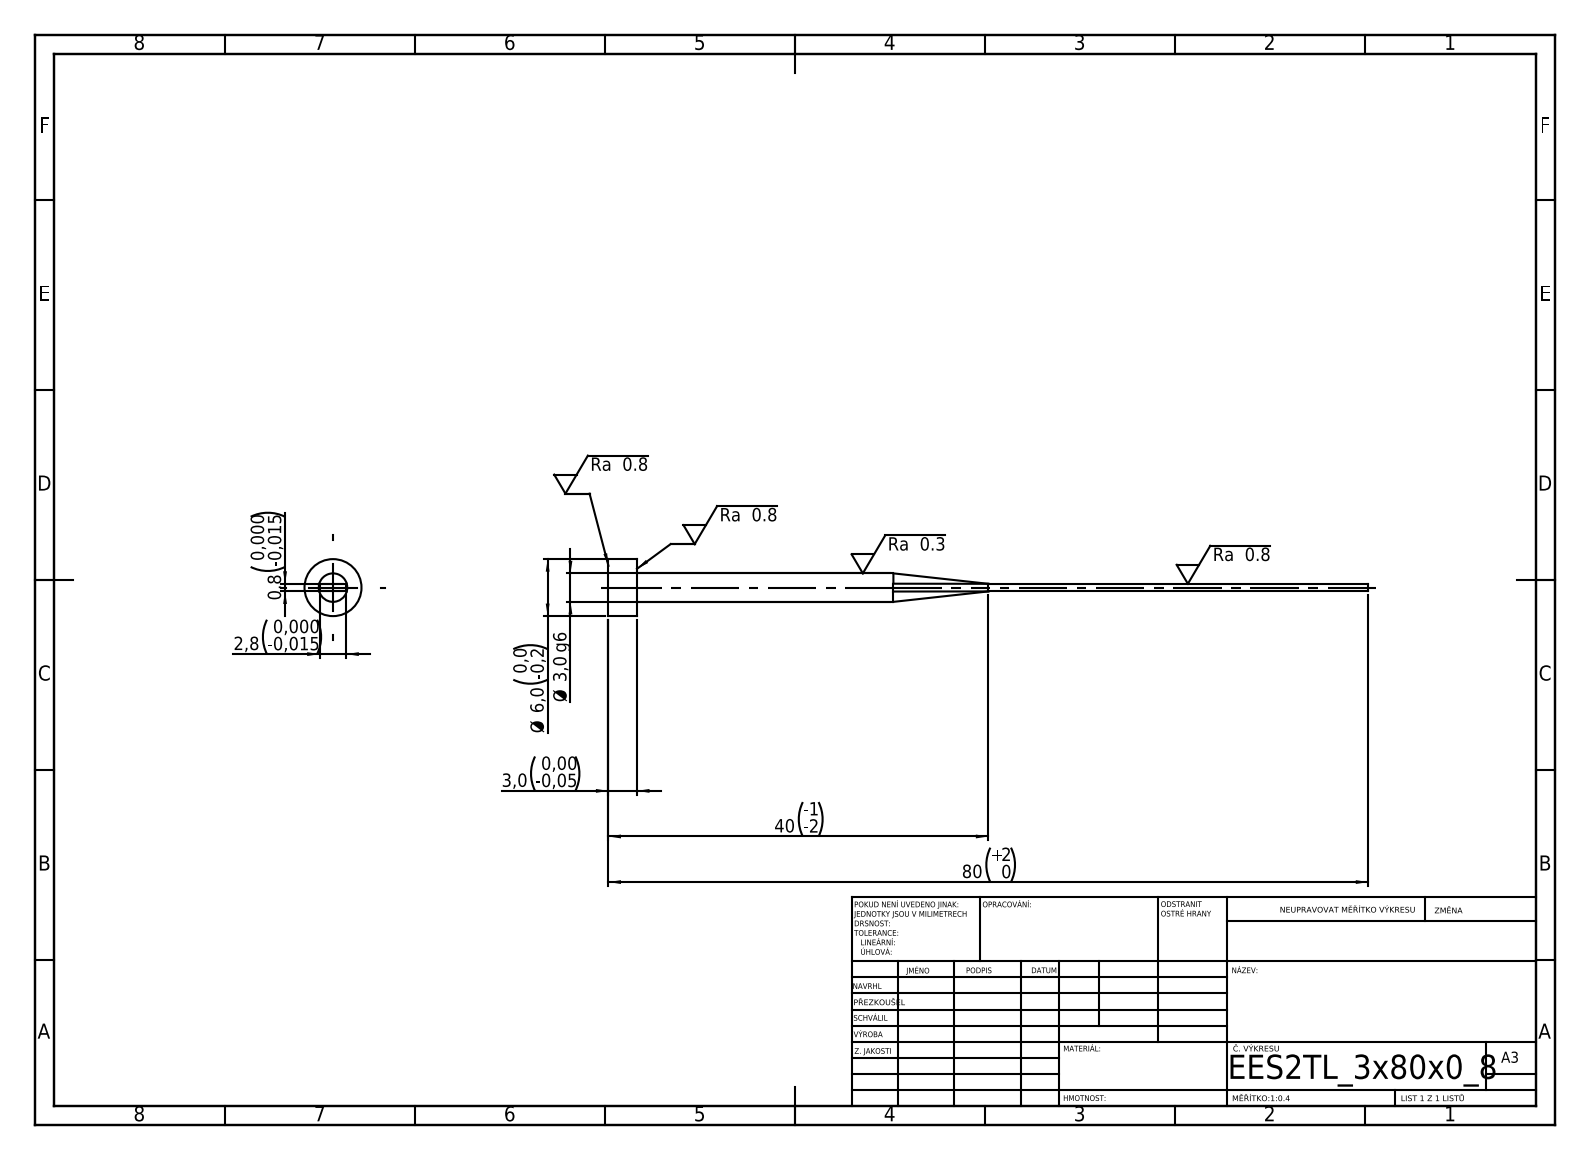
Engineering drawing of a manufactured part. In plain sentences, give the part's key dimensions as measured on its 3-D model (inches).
Its 3-D file was written by "SolidWorks 2019 (CONFIG_CONTROL_DESIGN)". It is 1 solid with 15 faces: 7 planar, 4 cylindrical and 4 other. Overall it measures 3.15 by 0.236 by 0.236 inches. Its volume is 0.025 cubic inches and its surface area 1.13 square inches. Round bosses or shafts: 1 of diameter 0.236, 1 of diameter 0.118. The main face-to-face distances are 0.031, 0.11, 0.118, 3.15, 3.031.
